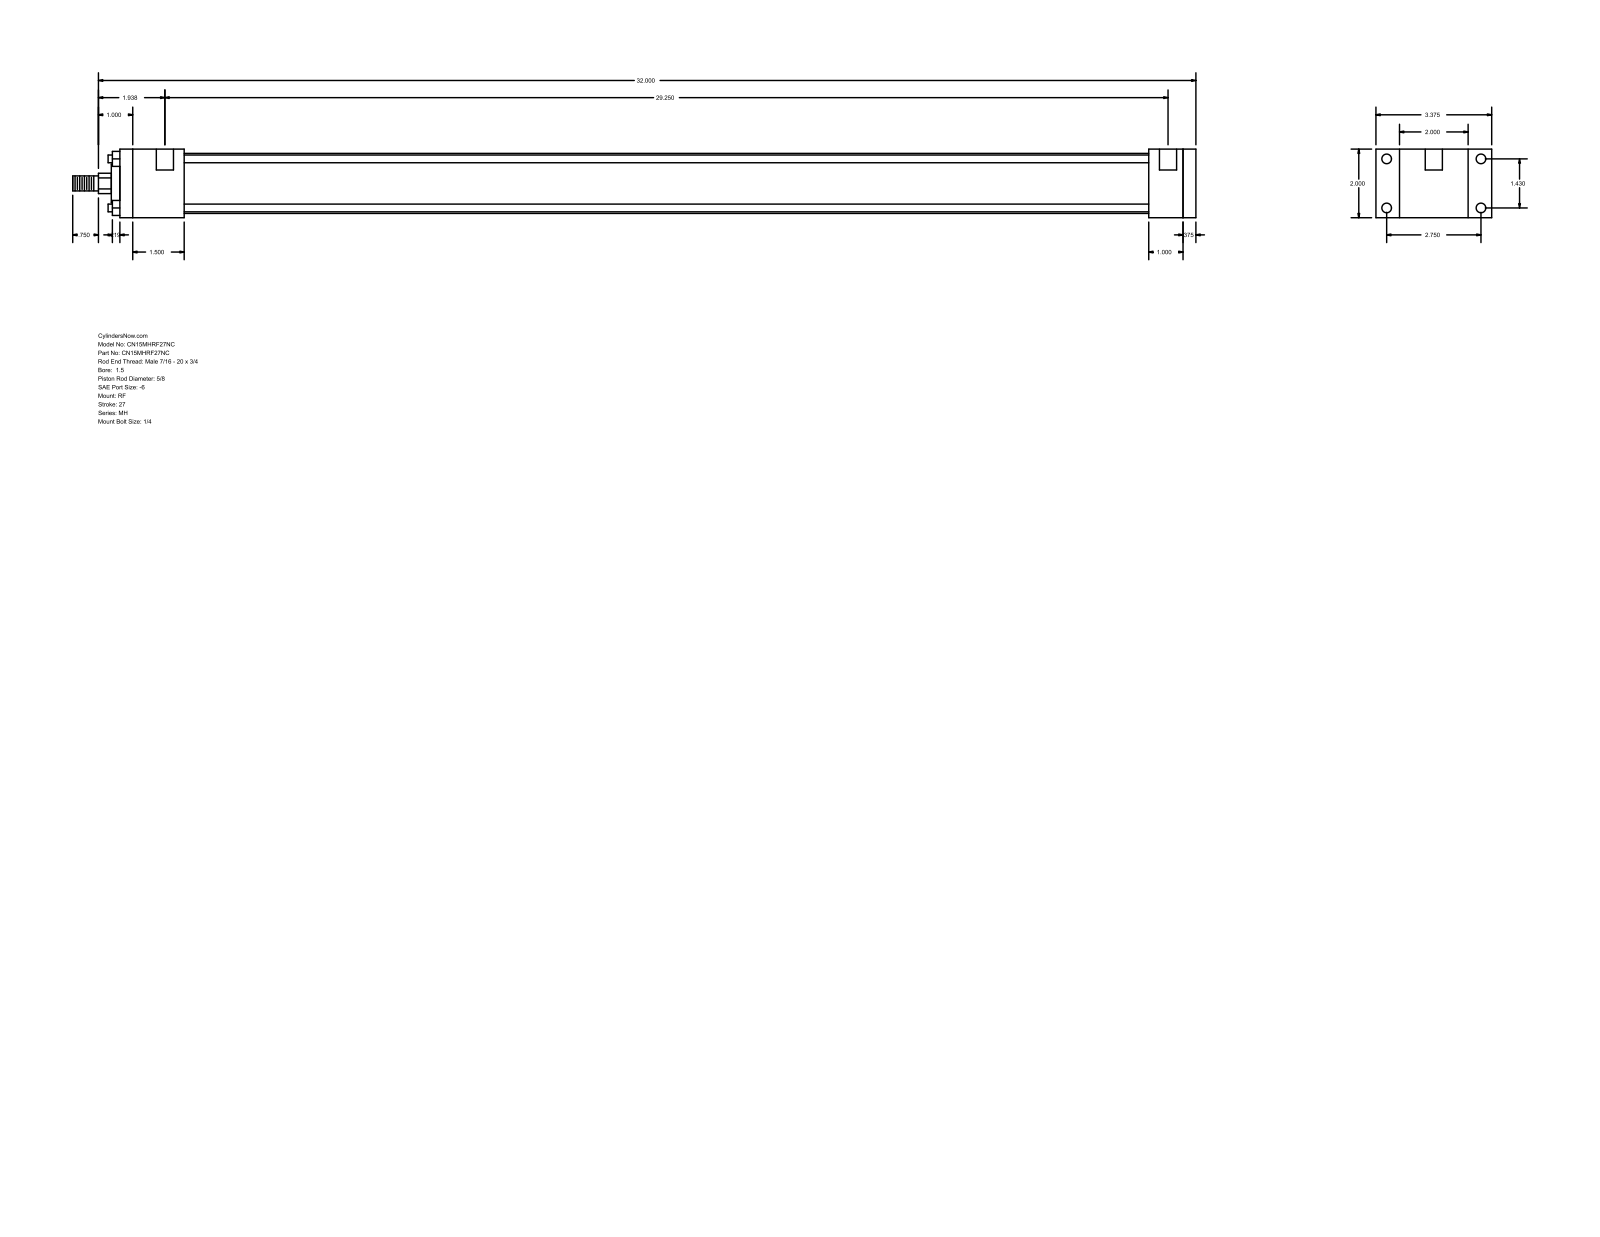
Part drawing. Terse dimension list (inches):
name: MH_RF__0150_0.625
written by: GSSL Pune (CONFIG_CONTROL_DESIGN)
unit: in
bodies: 0 solids, 92 faces (64 planar, 28 cylindrical, 0 other)
size: 32.75 × 3.375 × 2
holes: 4× ⌀0.219, 4× ⌀0.281, 2× ⌀0.5
bosses: 4× ⌀0.225, 1× ⌀1.75, 1× ⌀1.125, 1× ⌀0.625, 1× ⌀0.437
rounds: 1× R0.297
face distances: 2, 0.375, 31.375, 31, 0.687, 2.687, 30, 1, 1.375, 1.875
hole spacings: 1.43, 2.75, 3.099, 29.375, 0.125, 29.25
